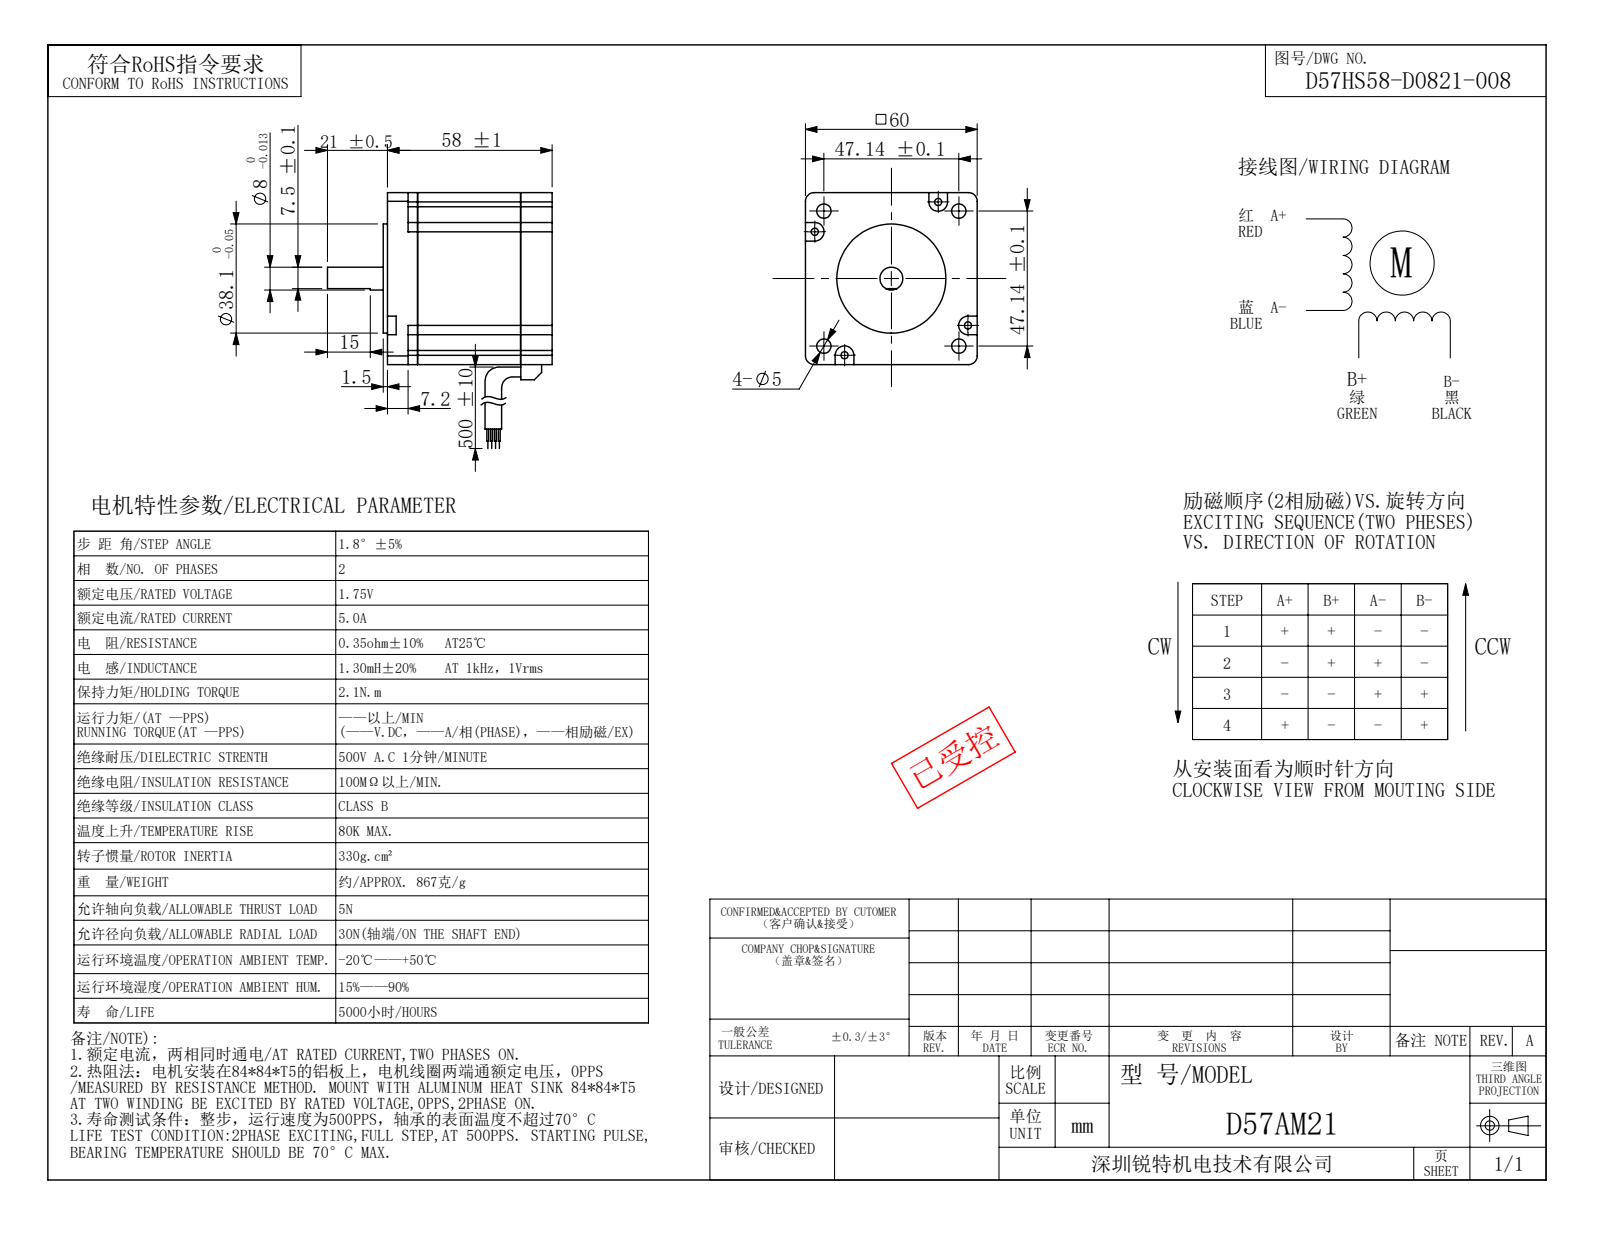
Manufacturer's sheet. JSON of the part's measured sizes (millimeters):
{"step_written_by": "SolidWorks 2014 (AUTOMOTIVE_DESIGN)", "units": "millimeters", "bodies": {"solids": 3, "faces": 246, "planar": 125, "cylindrical": 121, "other": 0}, "overall_size": [78.5, 60, 60], "volume_mm3": 73350, "surface_area_mm2": 43064, "round_holes": [[2.5, 4], [3.5, 4], [5, 4], [13, 1], [15.4, 1], [17.8, 1], [18, 1], [22, 1], [56, 1]], "round_bosses_or_shafts": [[40, 1], [39, 1], [38.1, 1], [8, 1]], "partial_cylinders_radius": [[3.25, 8], [3, 4], [3.3, 4], [5.5, 4]], "face_to_face_distances": [60, 57.5, 2.6, 44.4, 8.4, 2, 6.5, 53.5, 4, 50.9], "hole_center_spacings": [7.89, 31.35, 33.33, 40.05, 44.34, 47.14, 50.84, 64.23]}
